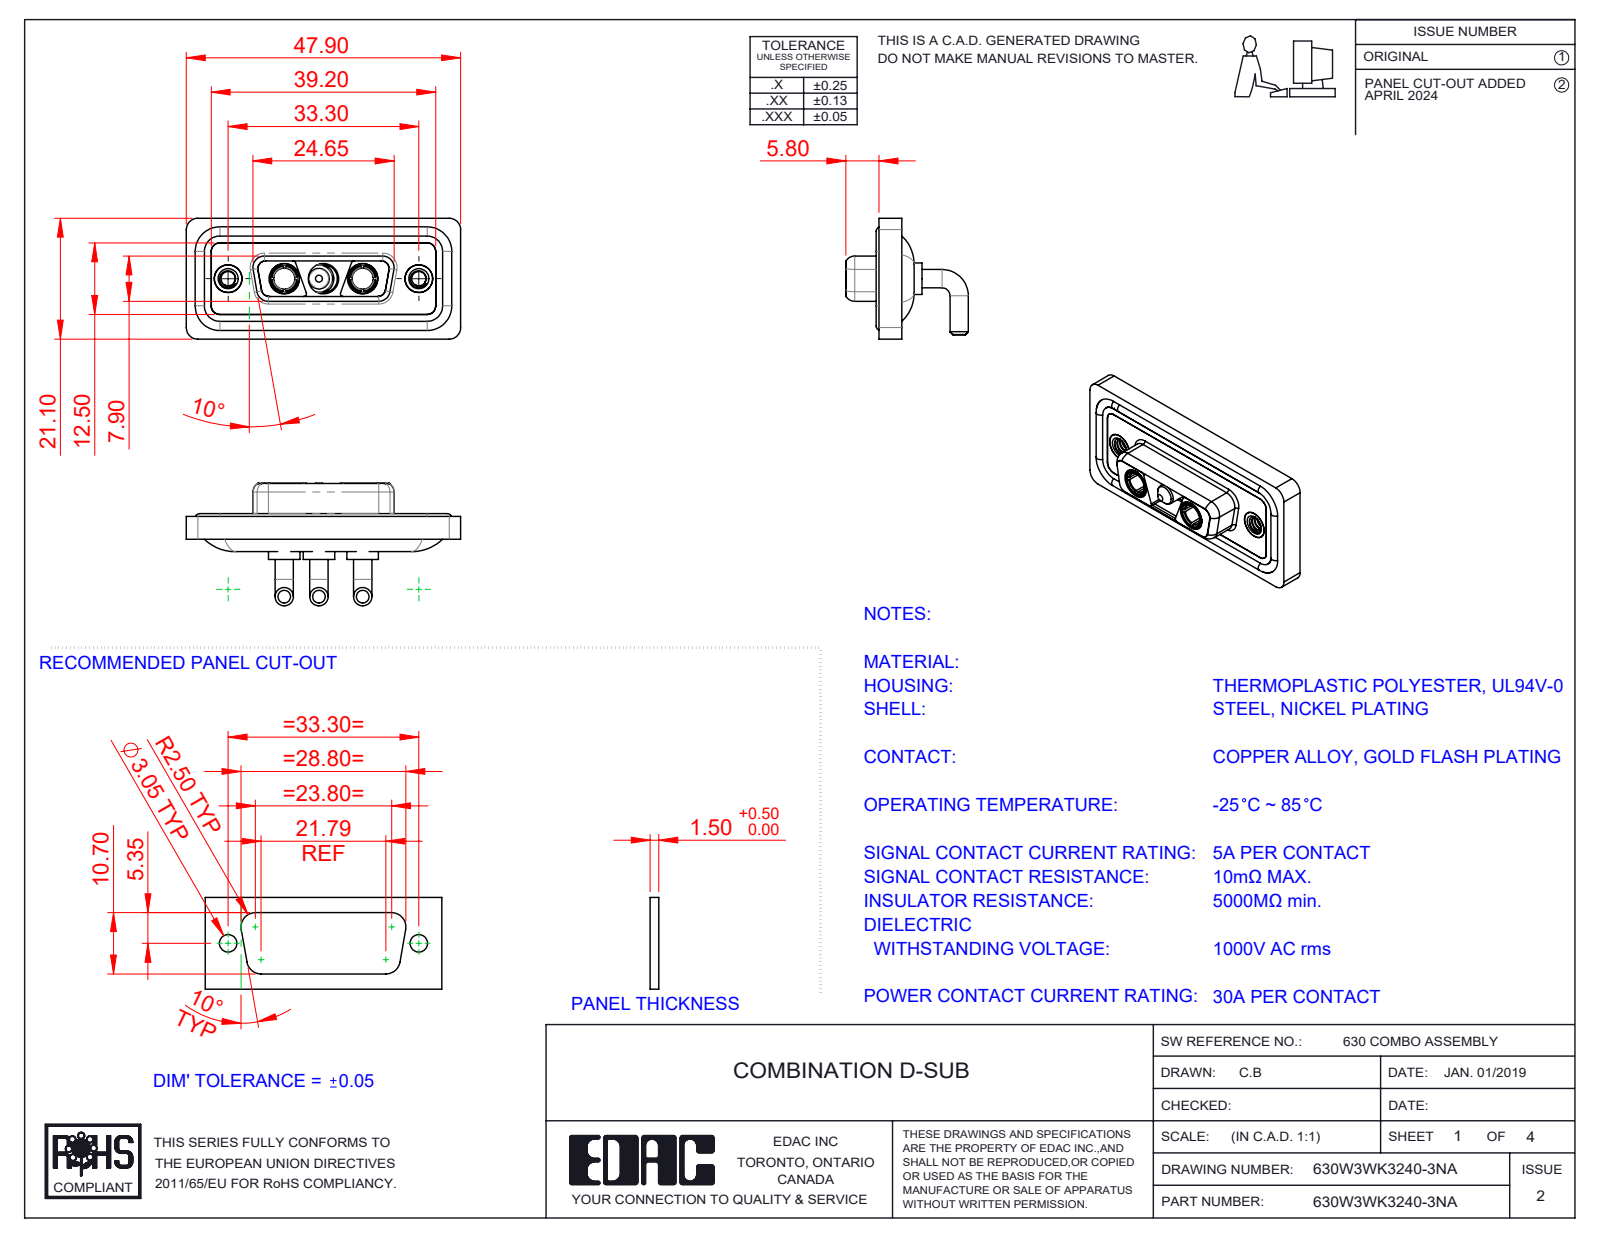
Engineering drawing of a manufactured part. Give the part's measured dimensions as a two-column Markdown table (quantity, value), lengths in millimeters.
| quantity | value |
| --- | --- |
| part name | 630Combo Threaded Rivet_A; 630Combo Shell Front_15 Contacts; 630Combo Waterproof Housing_15 Contacts; Power Socket_30A RA (+4 more) |
| STEP written by | SolidWorks 2023 (CONFIG_CONTROL_DESIGN) |
| units | millimeters |
| bodies | 13 solids, 589 faces (178 planar, 262 cylindrical, 149 other) |
| overall size | 47.9 × 21.4 × 21.1 |
| volume | 6 109 mm³ |
| surface area | 9 797 mm² |
| round holes (diameter × count) | 4.85 × 5, 5.3 × 3, 2.5 × 2, 3.7 × 2, 4 × 2, 4.05 × 2, 5 × 2 |
| round bosses / shafts (diameter × count) | 3.2 × 6, 1.6 × 4, 5.5 × 3, 5.2 × 3, 4.75 × 3, 3.75 × 3, 4.96 × 2, 4.95 × 2 |
| partial cylindrical surfaces (radius × count) | 2 × 20, 1.5 × 18, 1.35 × 12, 0.5 × 8, 1.6 × 8, 0.25 × 4, 0.6 × 4, 0.65 × 4 |
| main face-to-face distances | 0.4, 1.8, 1.1, 1.6, 2.9, 2.5, 3.1, 3.7, 4.1, 1.5 |
| hole center spacings | 6.85, 9.8, 16.65, 23.5, 13.7, 33.3 |
